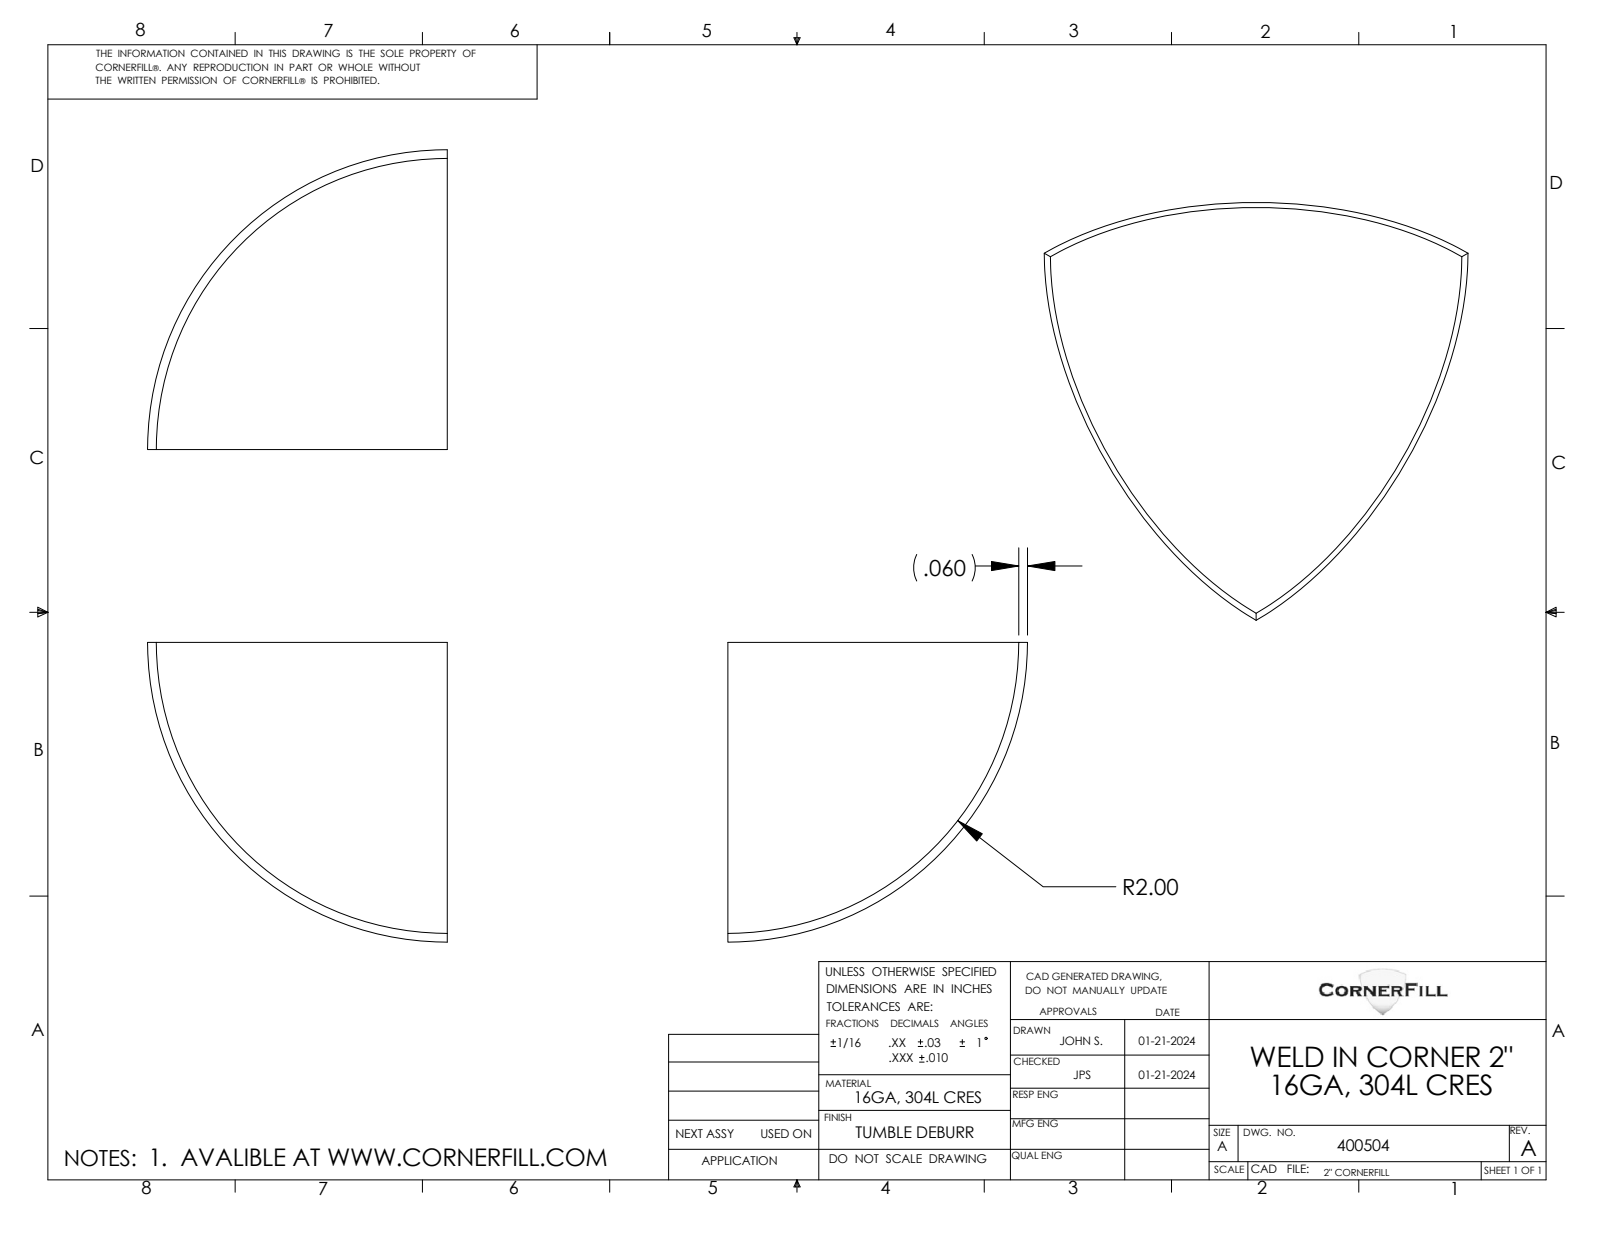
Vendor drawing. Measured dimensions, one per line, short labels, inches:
name: 400504
written by: SolidWorks 2021 (CONFIG_CONTROL_DESIGN)
unit: in
bodies: 1 solid, 5 faces (3 planar, 0 cylindrical, 2 other)
size: 2.913 × 2.06 × 2.06
volume: 0.388 in³; area: 13.52 in²
